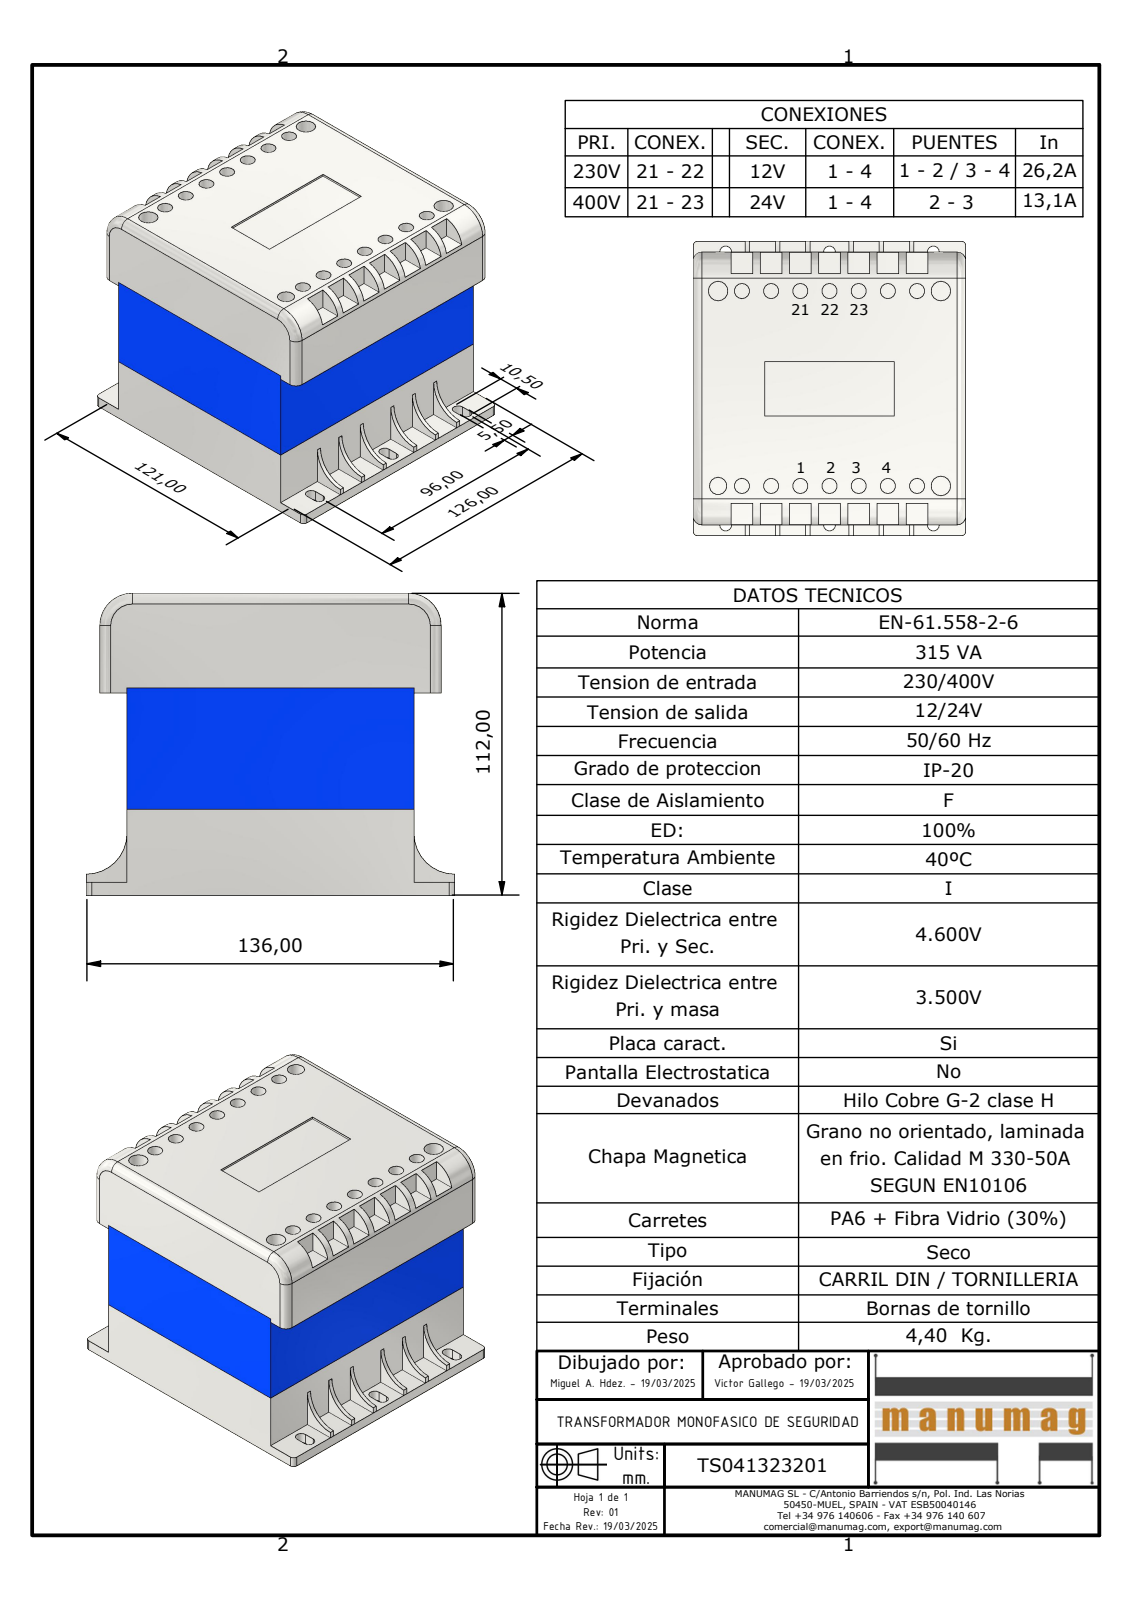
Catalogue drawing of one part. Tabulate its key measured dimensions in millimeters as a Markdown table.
| quantity | value |
| --- | --- |
| part name | TS041323201; INFERIOR EI120; CENTRAL EI120-40; SUPERIOR EI120 |
| STEP written by | Autodesk Inventor 2023 (AUTOMOTIVE_DESIGN) |
| units | millimeters |
| bodies | 15 solids, 244 faces (186 planar, 54 cylindrical, 4 other) |
| overall size | 136 × 126 × 109 |
| volume | 650 729 mm³ |
| surface area | 160 492 mm² |
| round holes (diameter × count) | 7 × 14, 9 × 3, 8 × 1 |
| partial cylindrical surfaces (radius × count) | 2.75 × 12, 4 × 6, 2 × 4, 12 × 2, 15 × 2 |
| main face-to-face distances | 1, 104, 5, 105, 126, 74, 125, 69, 106, 109 |
| hole center spacings | 13.5, 91.01, 27, 93.96, 90, 40.5, 98.69, 54 |
